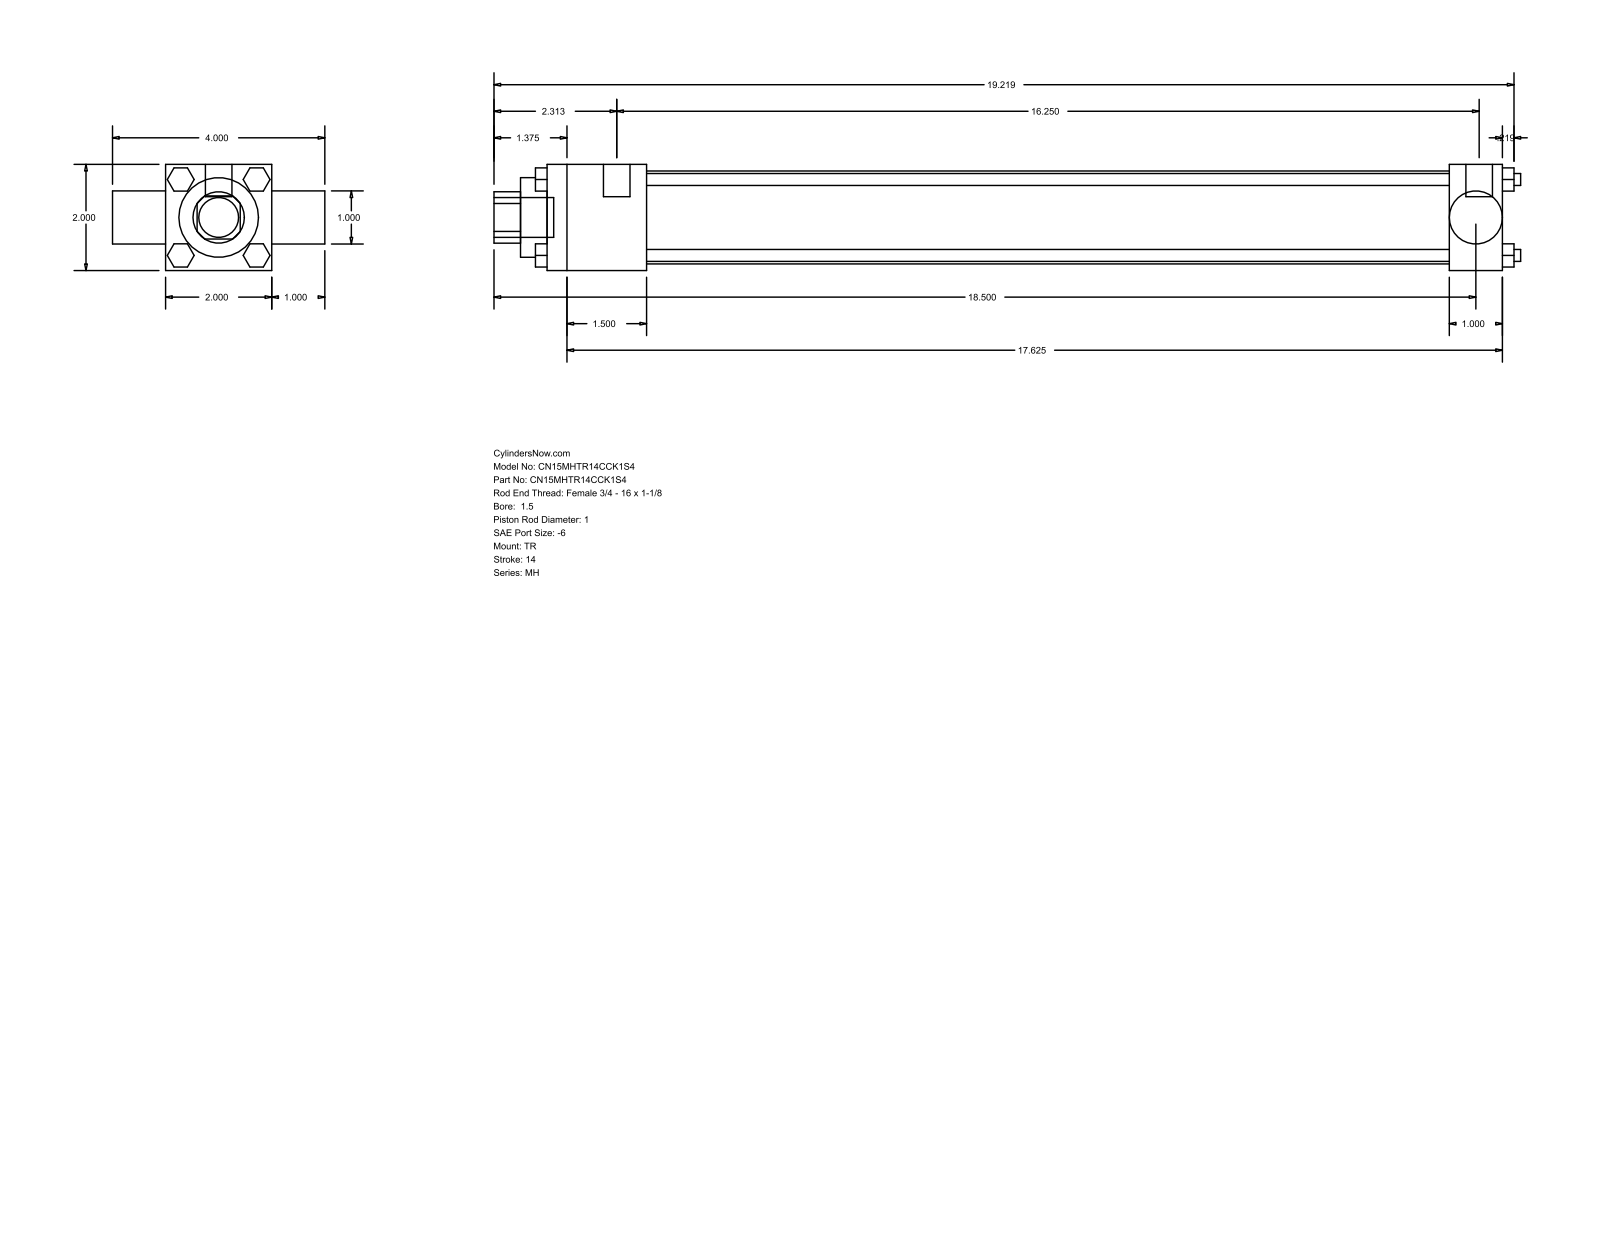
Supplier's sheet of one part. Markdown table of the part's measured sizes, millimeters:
| quantity | value |
| --- | --- |
| part name | MH_TR__0150_1 |
| STEP written by | GSSL Pune (CONFIG_CONTROL_DESIGN) |
| units | millimeters |
| bodies | 0 solids, 120 faces (92 planar, 28 cylindrical, 0 other) |
| overall size | 491.33 × 101.6 × 50.8 |
| round holes (diameter × count) | 25.35 × 1, 25.4 × 1, 38.1 × 1, 44.45 × 1 |
| round bosses / shafts (diameter × count) | 5.71 × 4, 5.56 × 3, 12.7 × 2, 19.05 × 1 |
| partial cylindrical surfaces (radius × count) | 12.29 × 1 |
| main face-to-face distances | 50.8, 25.4, 457.2, 76.2, 47.63, 409.57, 431.8, 384.17, 462.76, 12.7 |
